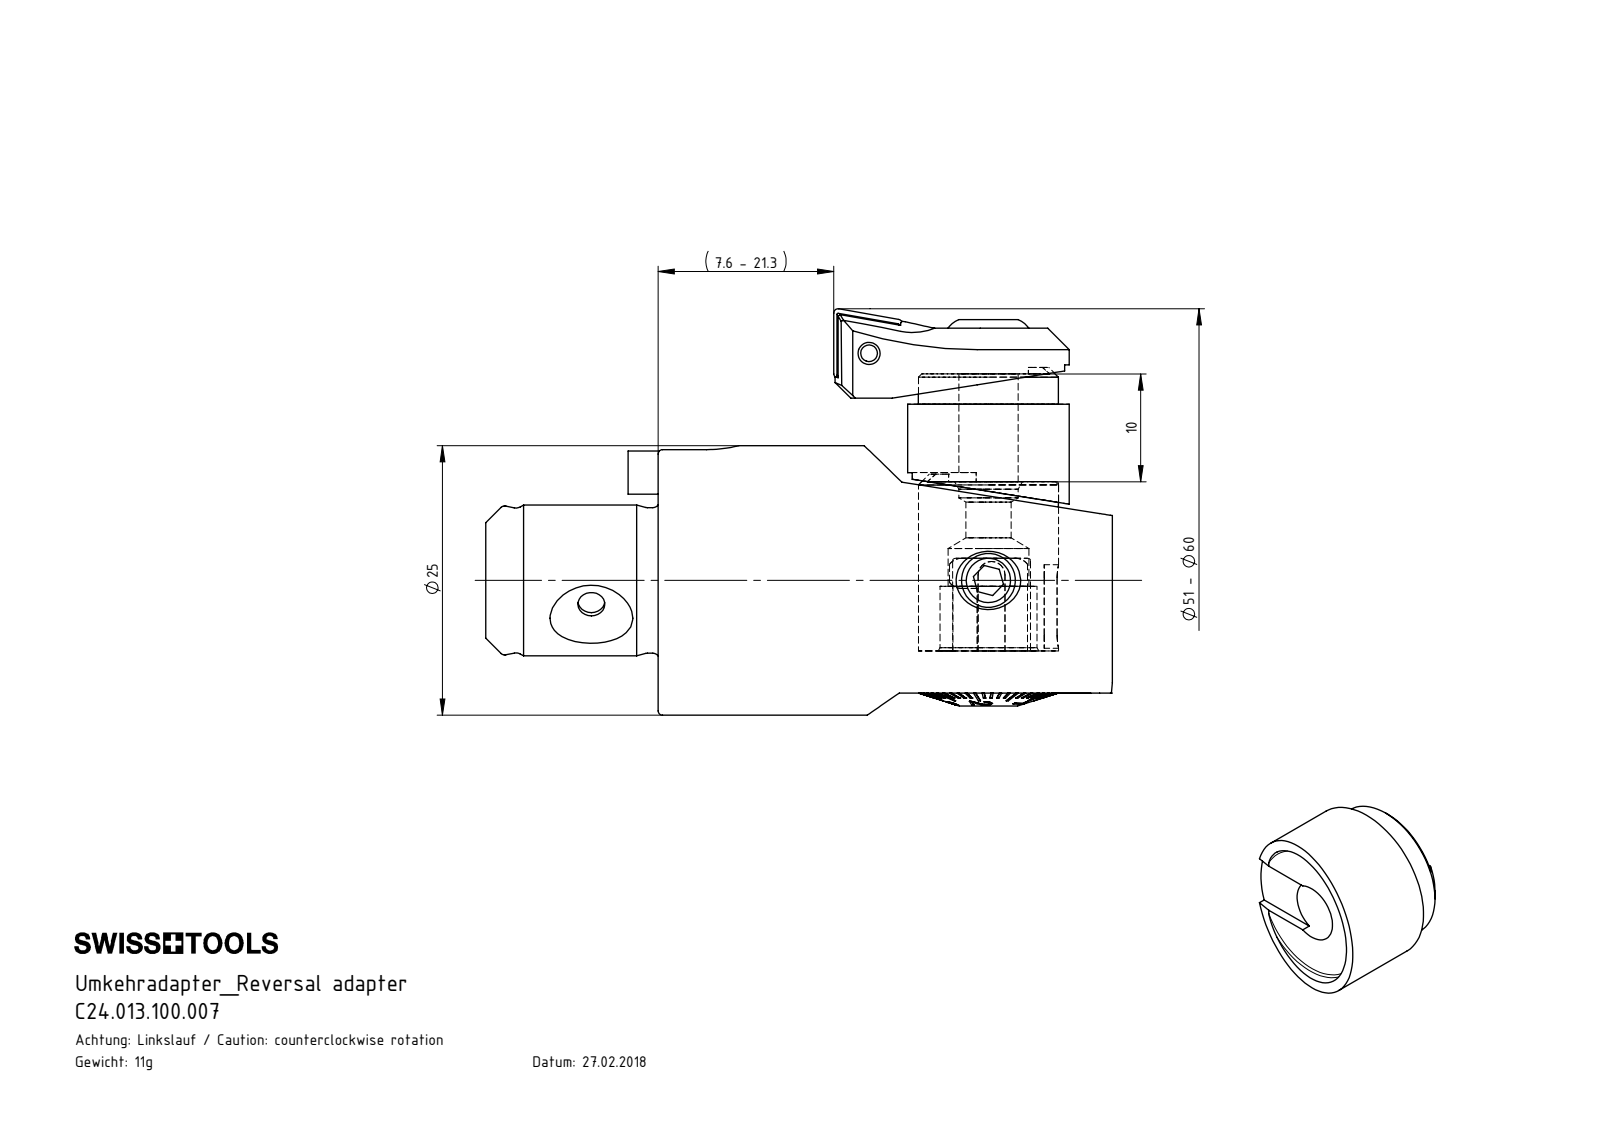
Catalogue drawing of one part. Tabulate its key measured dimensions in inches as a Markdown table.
| quantity | value |
| --- | --- |
| part name | F25-U00.001.010_B; C24.013.100.007 |
| STEP written by | SolidWorks 2017 (CONFIG_CONTROL_DESIGN) |
| units | inches |
| bodies | 1 solid, 27 faces (11 planar, 11 cylindrical, 5 other) |
| overall size | 0.591 × 0.591 × 0.499 |
| volume | 0.087 in³ |
| surface area | 1.564 in² |
| round holes (diameter × count) | 0.217 × 1, 0.512 × 1 |
| round bosses / shafts (diameter × count) | 0.591 × 1 |
| partial cylindrical surfaces (radius × count) | 0.02 × 2 |
| main face-to-face distances | 0.394, 0.11, 0.283, 0.36, 0.25, 0.033, 0.024, 0.134, 0.384, 0.417 |
